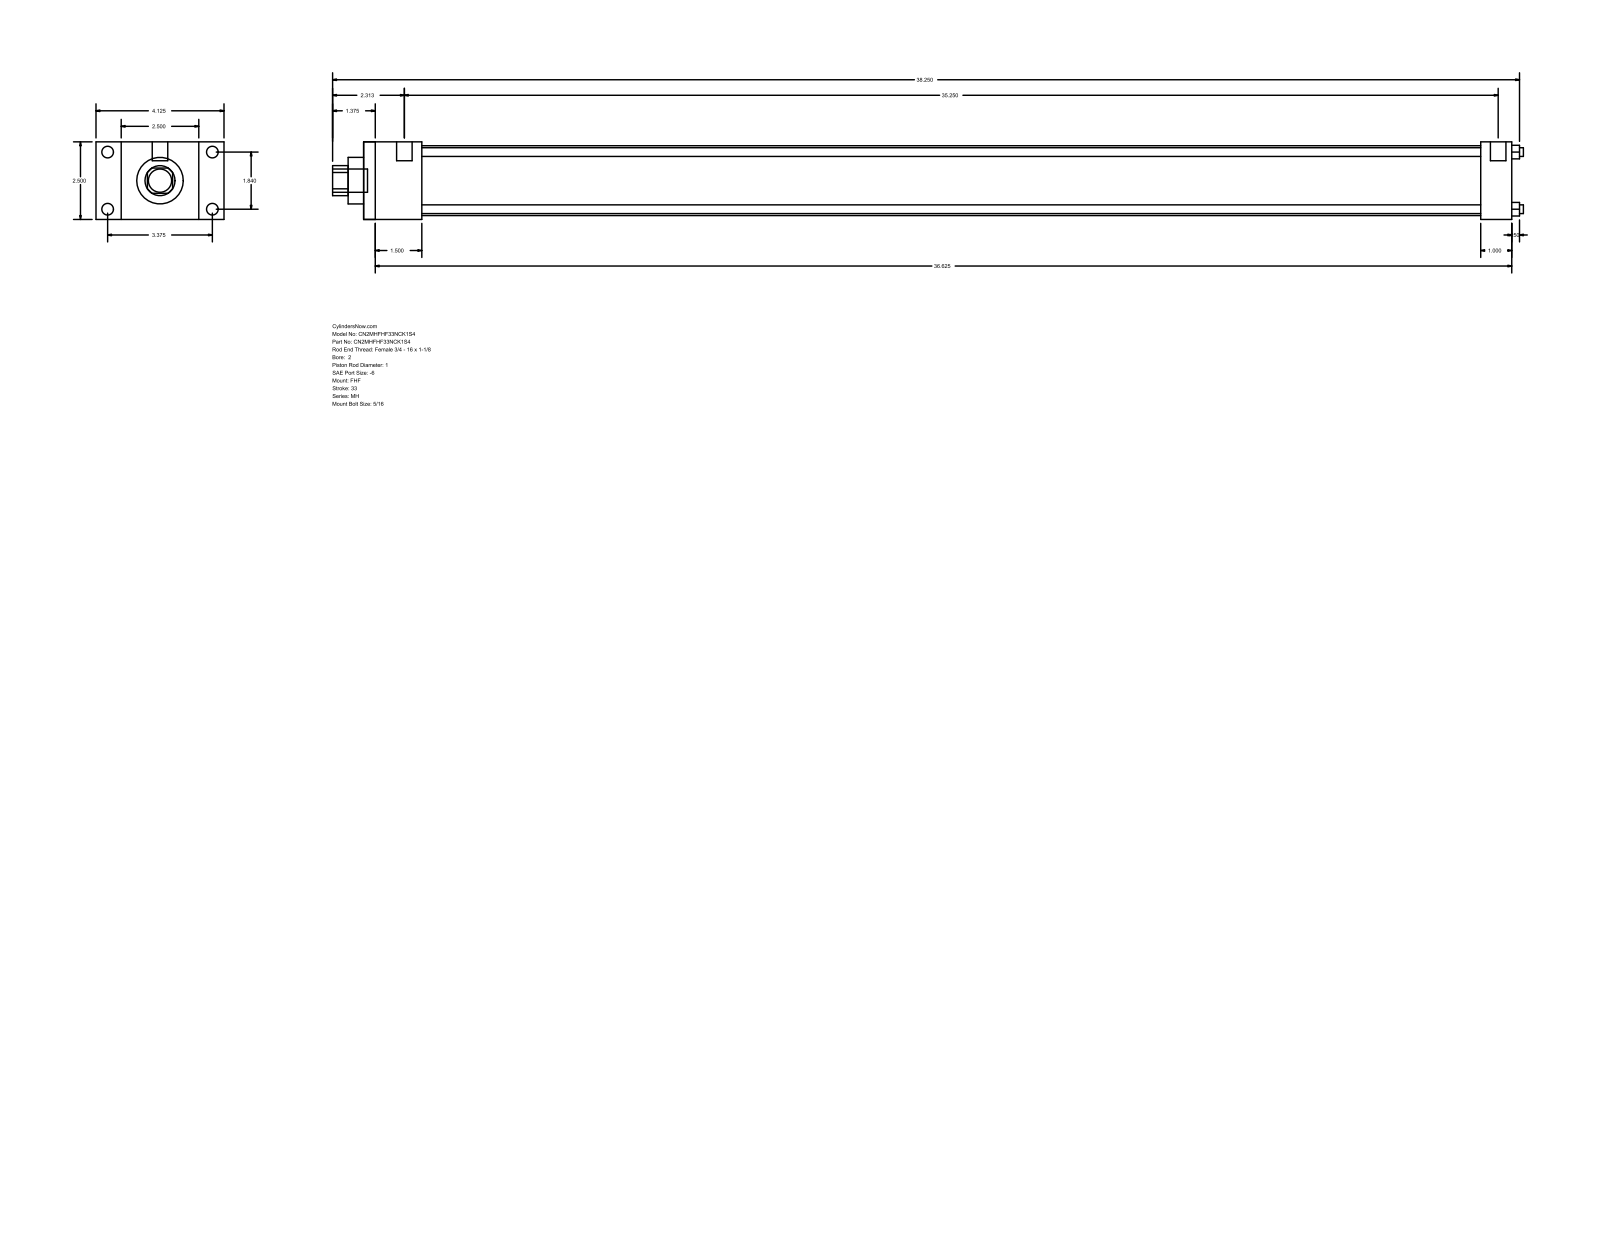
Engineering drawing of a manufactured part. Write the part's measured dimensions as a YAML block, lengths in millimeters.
part_name: "MH_FHF__0200_1"
step_written_by: "GSSL Pune (CONFIG_CONTROL_DESIGN)"
units: millimeters
bodies: {solids: 0, faces: 88, planar: 60, cylindrical: 28, other: 0}
overall_size: [974.73, 104.78, 63.5]
round_holes:
  - {diameter: 7.14, count: 4}
  - {diameter: 25.4, count: 1}
  - {diameter: 38.1, count: 1}
  - {diameter: 57.15, count: 1}
round_bosses_or_shafts:
  - {diameter: 9.53, count: 4}
  - {diameter: 5.56, count: 4}
  - {diameter: 12.7, count: 2}
  - {diameter: 19.05, count: 1}
partial_cylinders:
  - {radius: 12.29, count: 1}
face_to_face_distances: [63.5, 939.8, 47.63, 892.17, 20.64, 84.14, 104.78, 25.4, 914.4, 866.77]
hole_center_spacings: [33.05, 46.74, 66.1]
